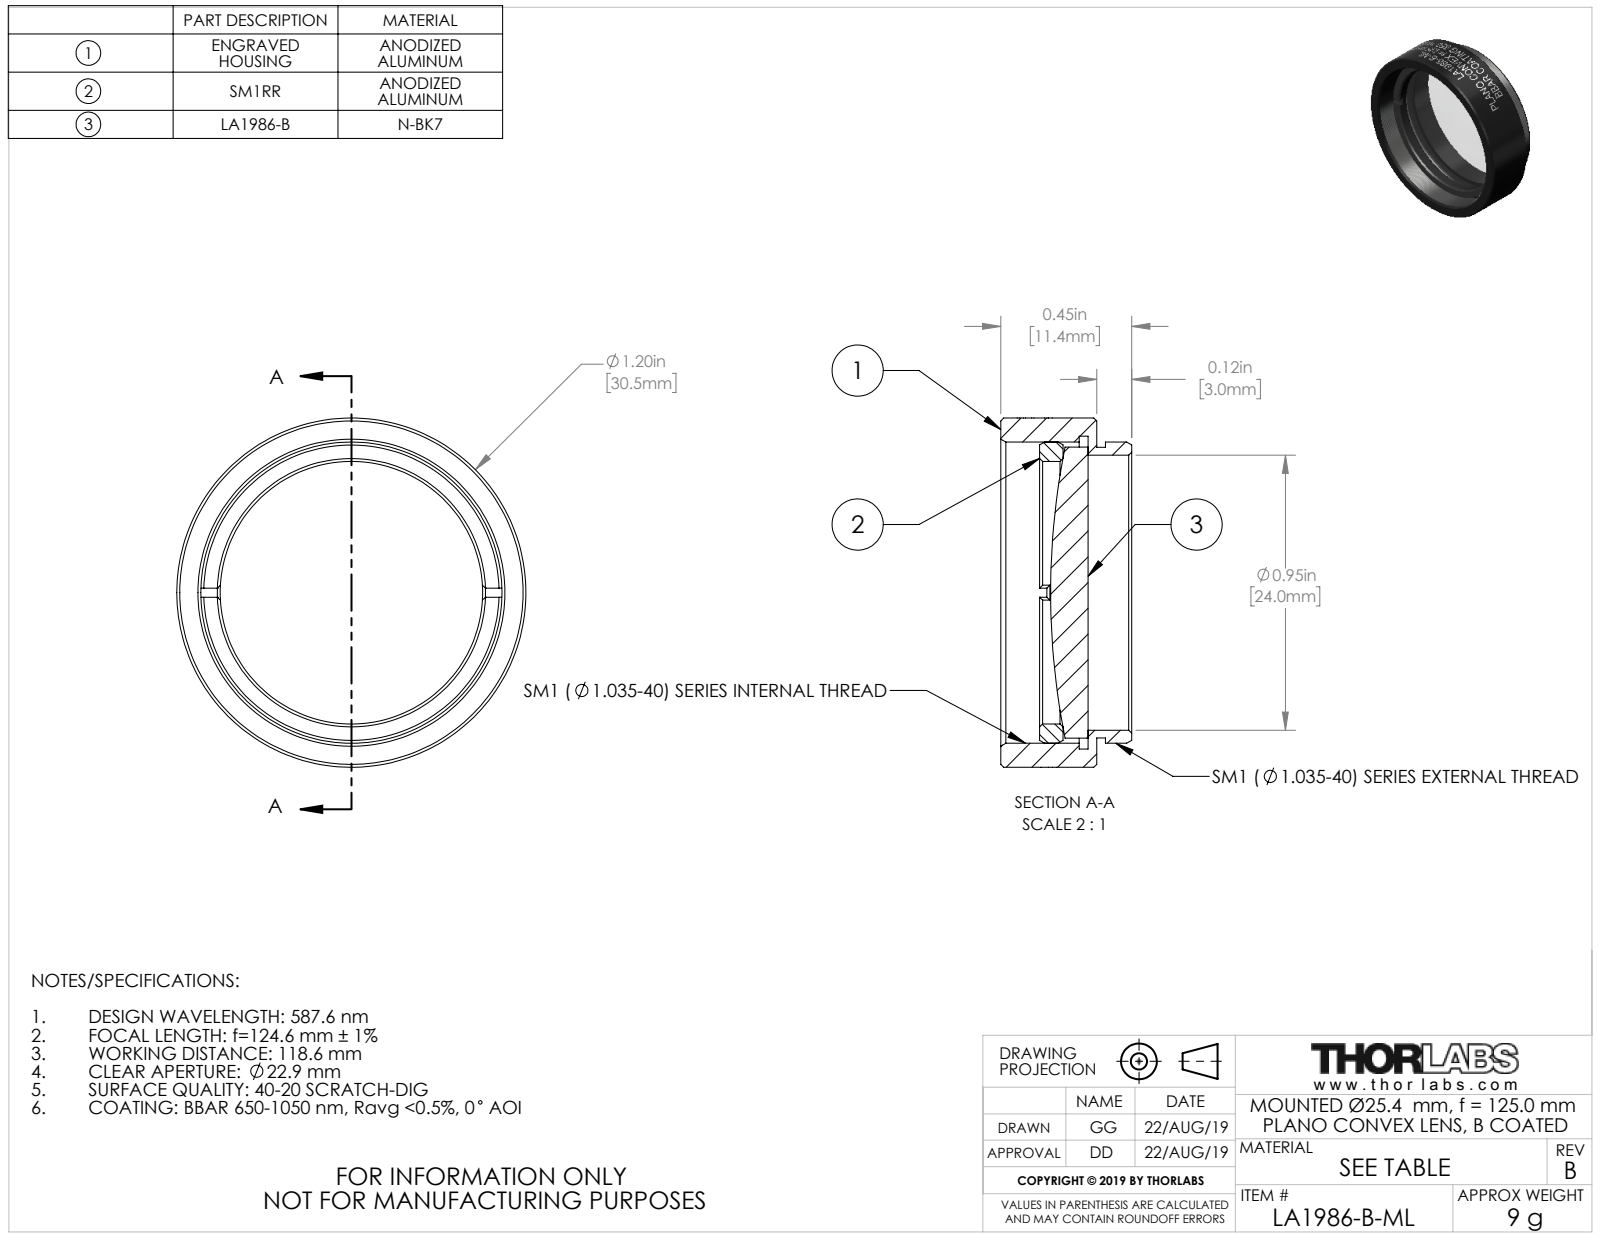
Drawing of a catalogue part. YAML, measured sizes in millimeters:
part_name: "24444-E0W"
step_written_by: "SolidWorks 2018 (CONFIG_CONTROL_DESIGN)"
units: millimeters
bodies: {solids: 3, faces: 156, planar: 20, cylindrical: 112, other: 24}
overall_size: [30.48, 30.48, 11.43]
volume: 3414
surface_area: 4317
round_holes:
  - {diameter: 22.91, count: 1}
  - {diameter: 24, count: 1}
  - {diameter: 27.3, count: 1}
round_bosses_or_shafts:
  - {diameter: 30.48, count: 1}
  - {diameter: 26.29, count: 1}
  - {diameter: 25.4, count: 1}
  - {diameter: 25.37, count: 1}
face_to_face_distances: [0.76, 8.38, 7.62, 2.95, 2.19, 5.43, 4.98, 4.22, 2.03, 3.4]
